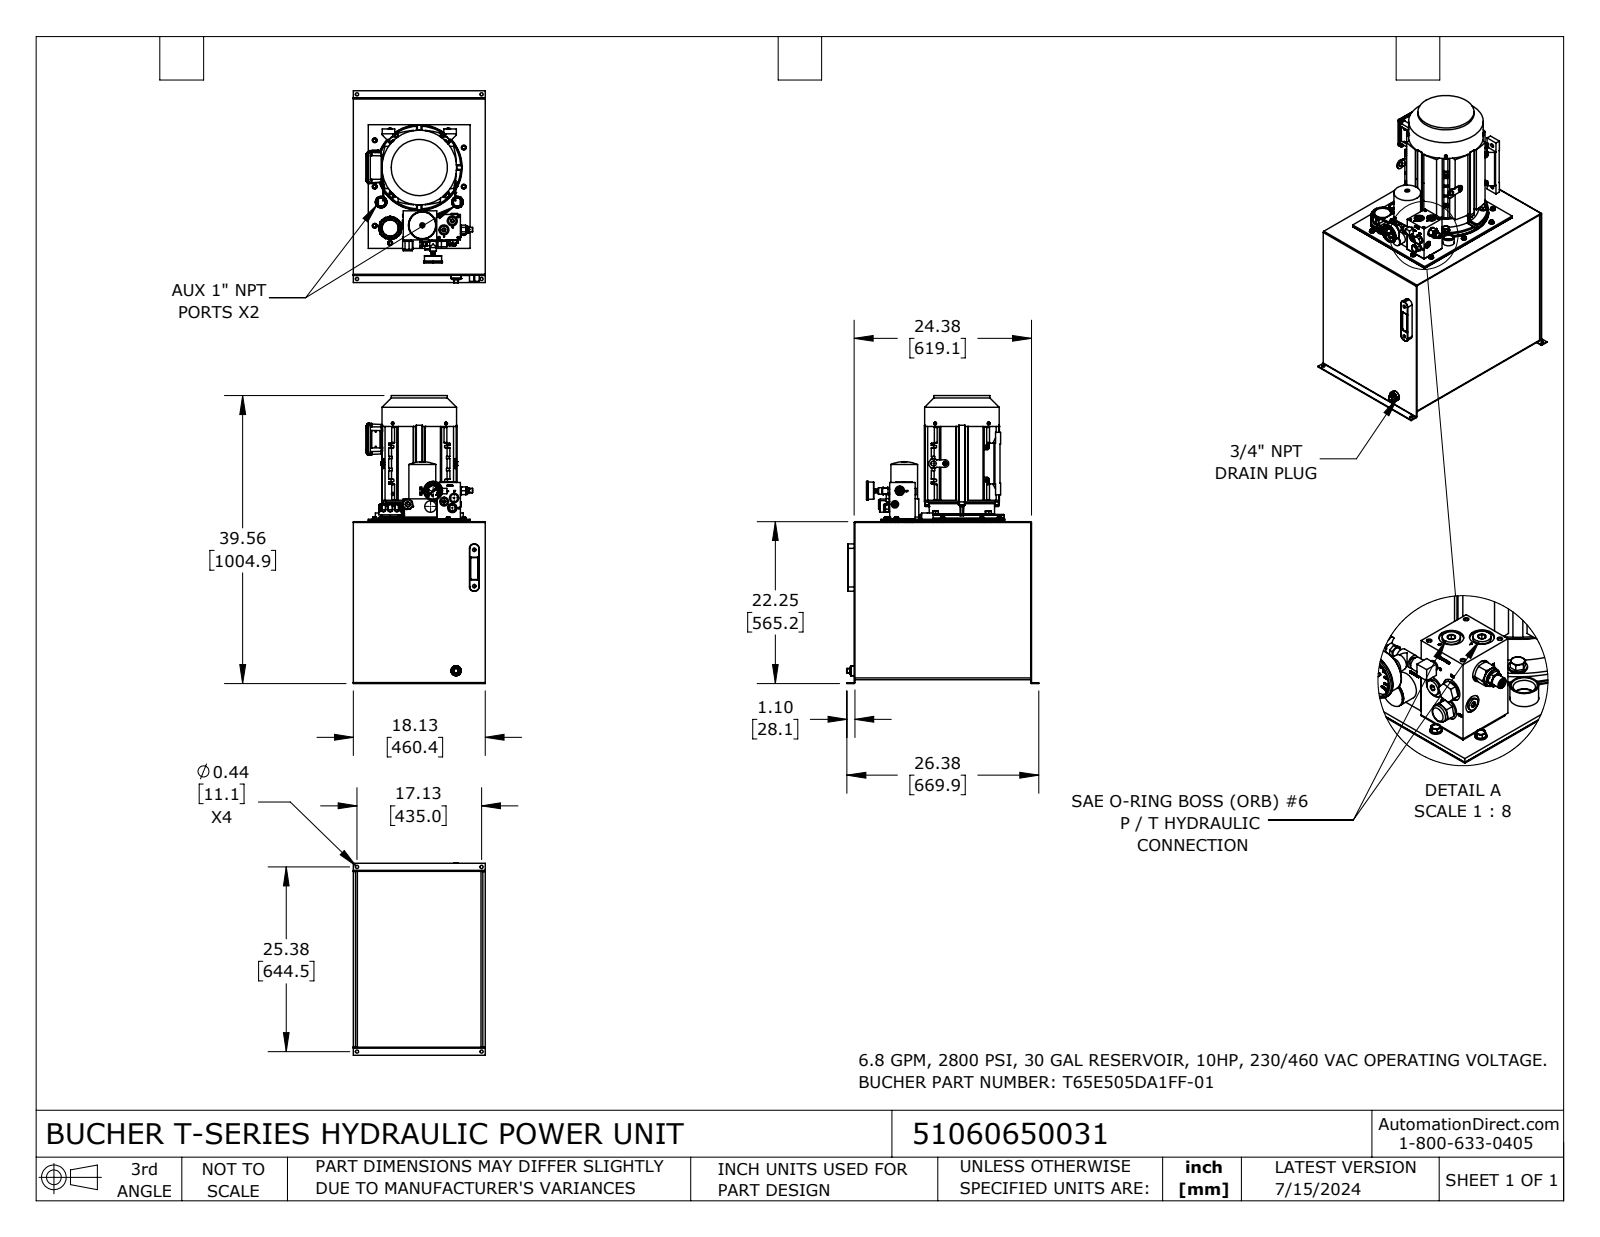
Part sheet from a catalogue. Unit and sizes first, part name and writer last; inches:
Units: inches
Overall size (bounding box): 39.562 × 26.4 × 18.125
Round holes (diameter × count): ⌀0.437 ×19, ⌀0.5 ×13, ⌀0.236 ×11, ⌀0.197 ×10, ⌀0.563 ×10, ⌀0.315 ×9, ⌀0.201 ×8, ⌀0.268 ×8, ⌀0.19 ×6, ⌀0.422 ×6, ⌀0.531 ×6, ⌀0.12 ×5
Round bosses / shafts (diameter × count): ⌀0.313 ×11, ⌀0.676 ×10, ⌀0.551 ×9, ⌀0.472 ×9, ⌀0.315 ×7, ⌀0.197 ×7, ⌀0.373 ×6, ⌀0.25 ×5
Partial cylindrical surfaces — rounded edges, fillets, slot ends (radius × count): R0.02 ×148, R0.079 ×68, R0.039 ×52, R0.118 ×52, R0.05 ×37, R0.25 ×36, R0.063 ×20, R0.375 ×15
Main face-to-face distances: 0.104, 24.27, 21.635, 0.105, 17.5, 17.395, 17.291, 17.396, 24.375, 24.166
Hole centre spacings: 3.469, 4.646, 4.764, 3.799, 6.232, 9.489, 9.137, 9.137
Volume: 1 865 in³ · Surface area: 8 039 in²
Bodies: 134 solids, 6510 faces (3305 planar, 1786 cylindrical, 1419 other)
Part name (STEP PRODUCT): 51060650031
STEP written by: SolidWorks 2023 (CONFIG_CONTROL_DESIGN)
